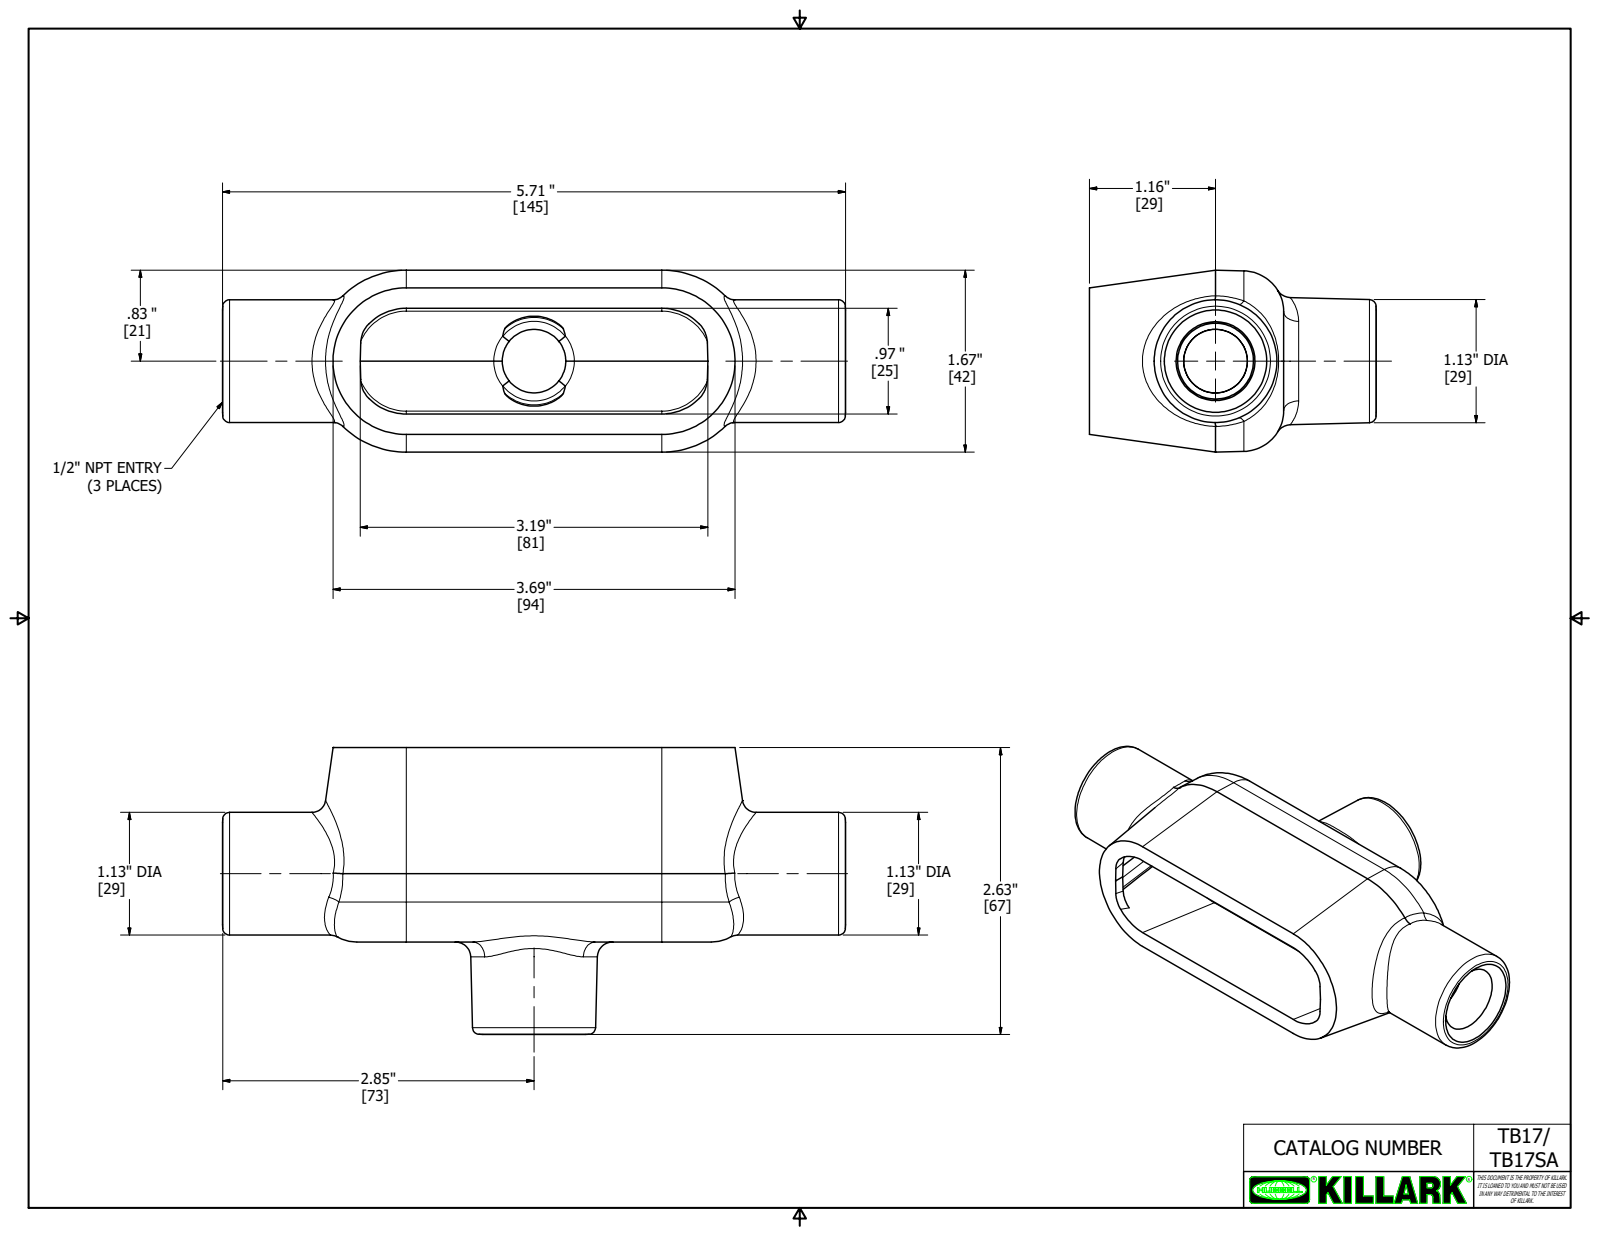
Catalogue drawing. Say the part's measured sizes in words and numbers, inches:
The part is named "17647-2". Its 3-D file was written by "Autodesk Inventor 2018 (AUTOMOTIVE_DESIGN)". It is 1 solid with 506 faces: 292 planar, 43 cylindrical and 171 other. Overall it measures 5.713 by 2.63 by 1.669 inches. Its volume is 4.907 cubic inches and its surface area 56.09 square inches. Round holes: 2 of diameter 0.844, 1 of diameter 0.047, 1 of diameter 0.407, 1 of diameter 0.859. Round bosses or shafts: 1 of diameter 1.125, 1 of diameter 0.5, 1 of diameter 0.056. Partial cylindrical surfaces (rounded edges, fillets, slot ends): 10 of radius 0.062, 3 of radius 0.187, 2 of radius 0.063, 2 of radius 0.375, 2 of radius 0.5, 1 of radius 0.006, 1 of radius 0.009, 1 of radius 0.016. The main face-to-face distances are 0.185, 1.781, 0.188, 0.031, 1.75, 0.217, 1.484, 0.25, 1.937, 3.187. The hole center spacings are 0.122.
